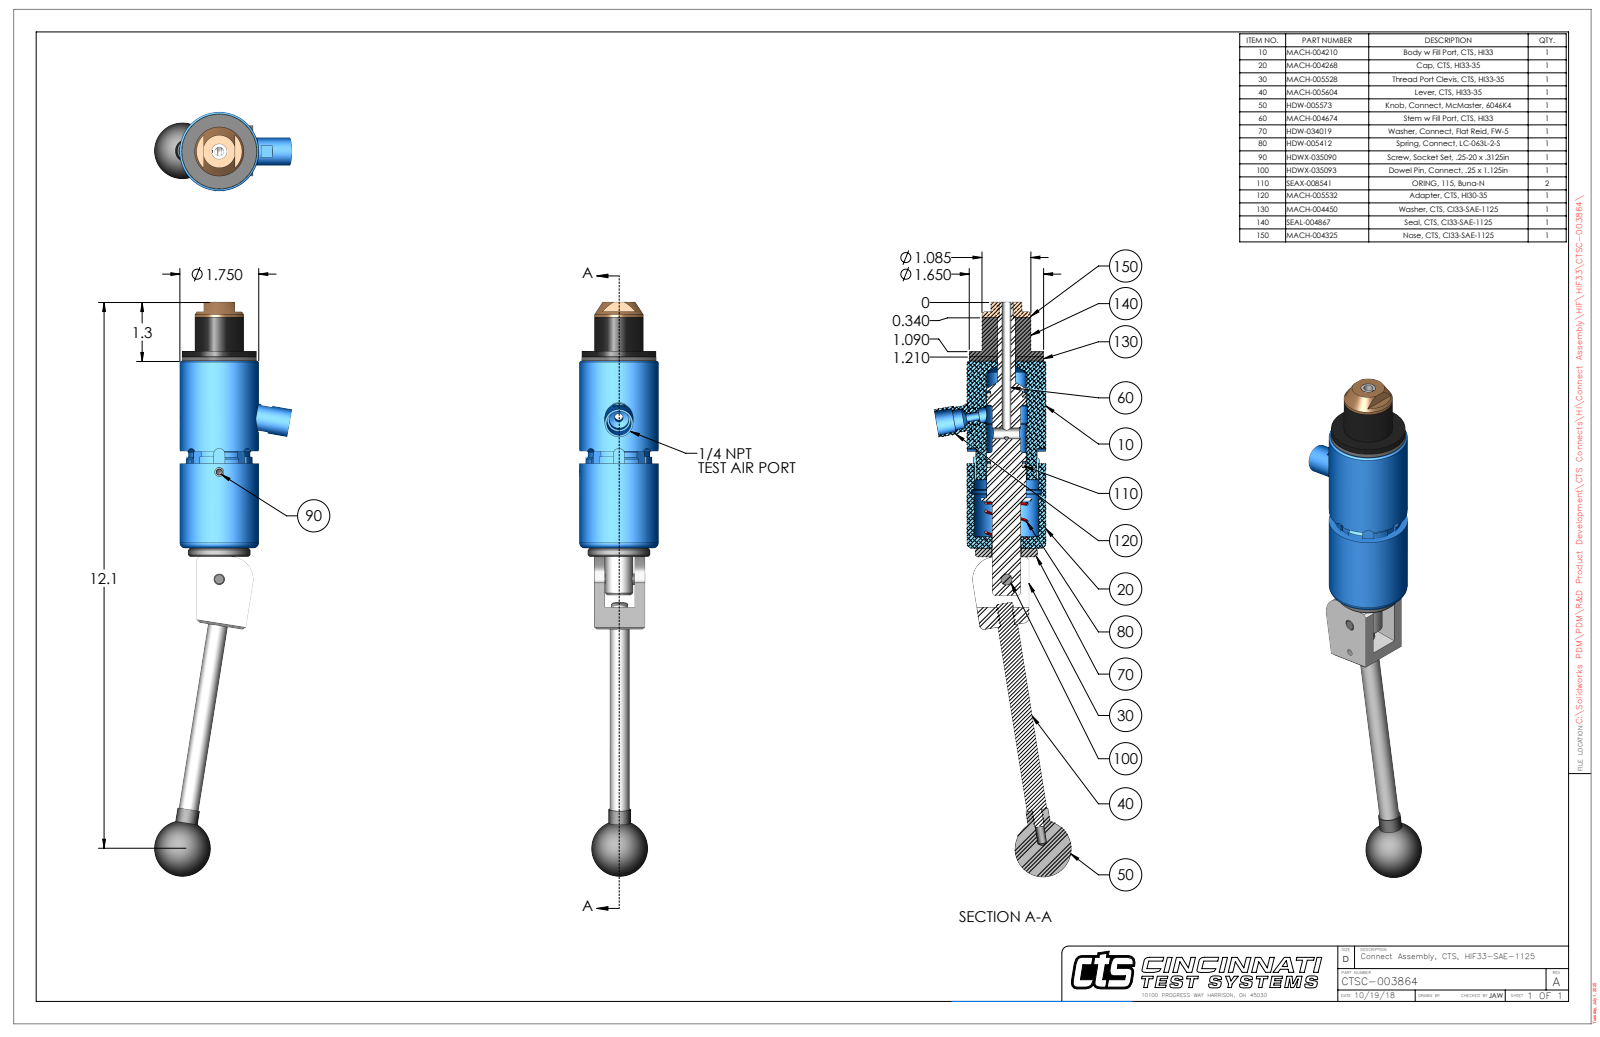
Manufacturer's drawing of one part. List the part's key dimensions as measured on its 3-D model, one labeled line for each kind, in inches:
Part name (STEP PRODUCT): CTSC-003864
STEP written by: SolidWorks 2023 (AUTOMOTIVE_DESIGN)
Units: inches
Bodies: 9 solids, 331 faces (120 planar, 140 cylindrical, 71 other)
Overall size (bounding box): 12.729 × 3.043 × 1.75
Volume: 14.44 in³ · Surface area: 81.95 in²
Round holes (diameter × count): ⌀0.201 ×2, ⌀0.313 ×2, ⌀0.15 ×1, ⌀0.187 ×1, ⌀0.204 ×1, ⌀0.249 ×1, ⌀0.25 ×1, ⌀0.251 ×1, ⌀0.39 ×1, ⌀0.397 ×1, ⌀0.403 ×1, ⌀0.438 ×1
Round bosses / shafts (diameter × count): ⌀0.312 ×2, ⌀0.25 ×2, ⌀1.75 ×1, ⌀1.65 ×1, ⌀1.38 ×1, ⌀1.085 ×1, ⌀0.625 ×1, ⌀0.62 ×1
Partial cylindrical surfaces — rounded edges, fillets, slot ends (radius × count): R0.125 ×4, R0.029 ×2, R0.149 ×1, R0.166 ×1, R0.166 ×1, R0.33 ×1, R0.5 ×1, R0.695 ×1
Main face-to-face distances: 0.098, 4.244, 4.146, 0.87, 0.968, 5.114, 1.12, 5.302, 4.432, 4.334
Hole centre spacings: 0.74, 2.376, 3.116
